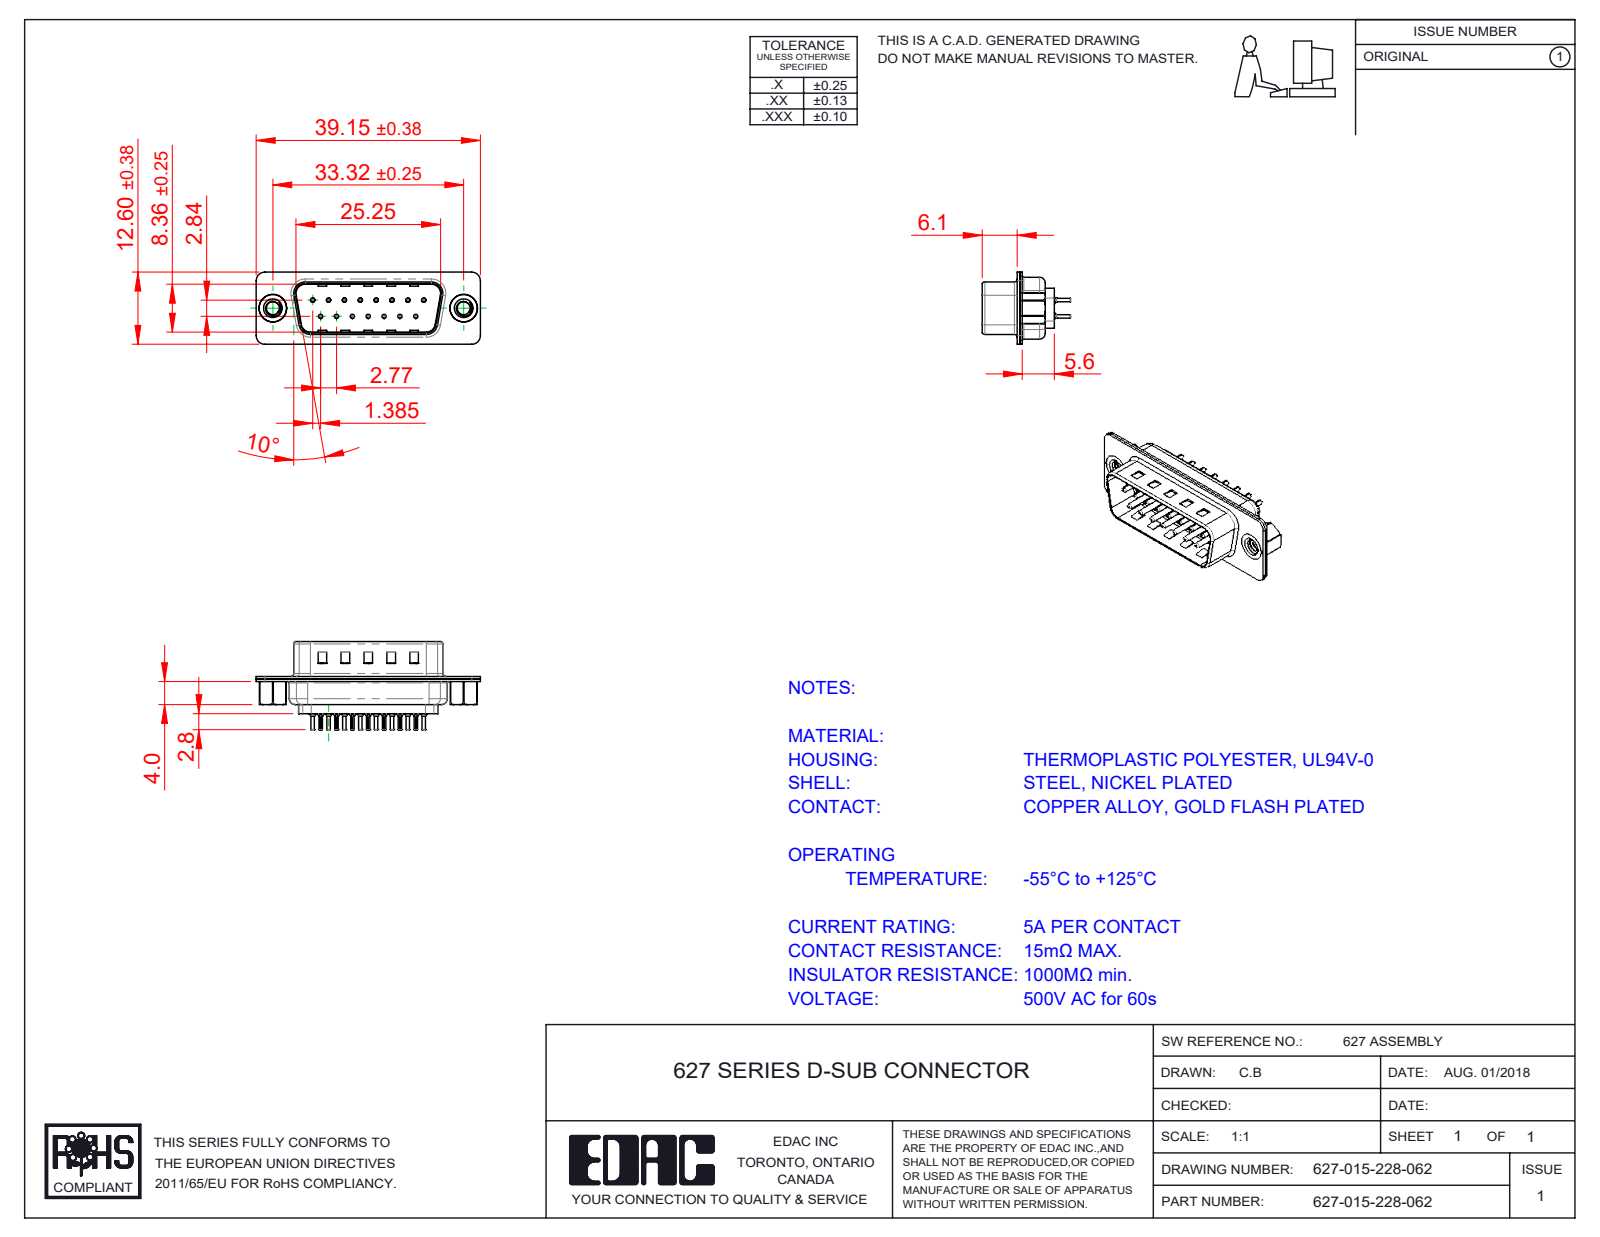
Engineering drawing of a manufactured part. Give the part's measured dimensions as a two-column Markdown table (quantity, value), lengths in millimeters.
| quantity | value |
| --- | --- |
| part name | 627 Shell Front_15 Contacts; 627 Contact Row 1_28L; 627-015-228-062; 627 Shell Rear_15 Contacts (+3 more) |
| STEP written by | SolidWorks 2020 (CONFIG_CONTROL_DESIGN) |
| units | millimeters |
| bodies | 21 solids, 1847 faces (505 planar, 721 cylindrical, 621 other) |
| overall size | 39.15 × 18.8 × 12.6 |
| volume | 2 205 mm³ |
| surface area | 6 089 mm² |
| round holes (diameter × count) | 0.2 × 15, 0.35 × 15, 1.1 × 15, 1.6 × 15, 2.26 × 2, 4 × 2, 4.8 × 2 |
| round bosses / shafts (diameter × count) | 2 × 15, 1.5 × 15, 0.75 × 15, 0.6 × 15, 5 × 2, 4.9 × 2 |
| partial cylindrical surfaces (radius × count) | 0.1 × 30, 1.5 × 16, 2 × 12, 0.5 × 8, 1.6 × 8, 0.25 × 4, 0.6 × 4, 0.65 × 4 |
| main face-to-face distances | 0.4, 0.45, 0.9, 6.05, 0.82, 9.58, 8.4, 6.5, 1.5, 2.8 |
| hole center spacings | 3.16, 2.77, 5.54, 8.31, 11.08, 5.03, 5.04, 7.48 |
